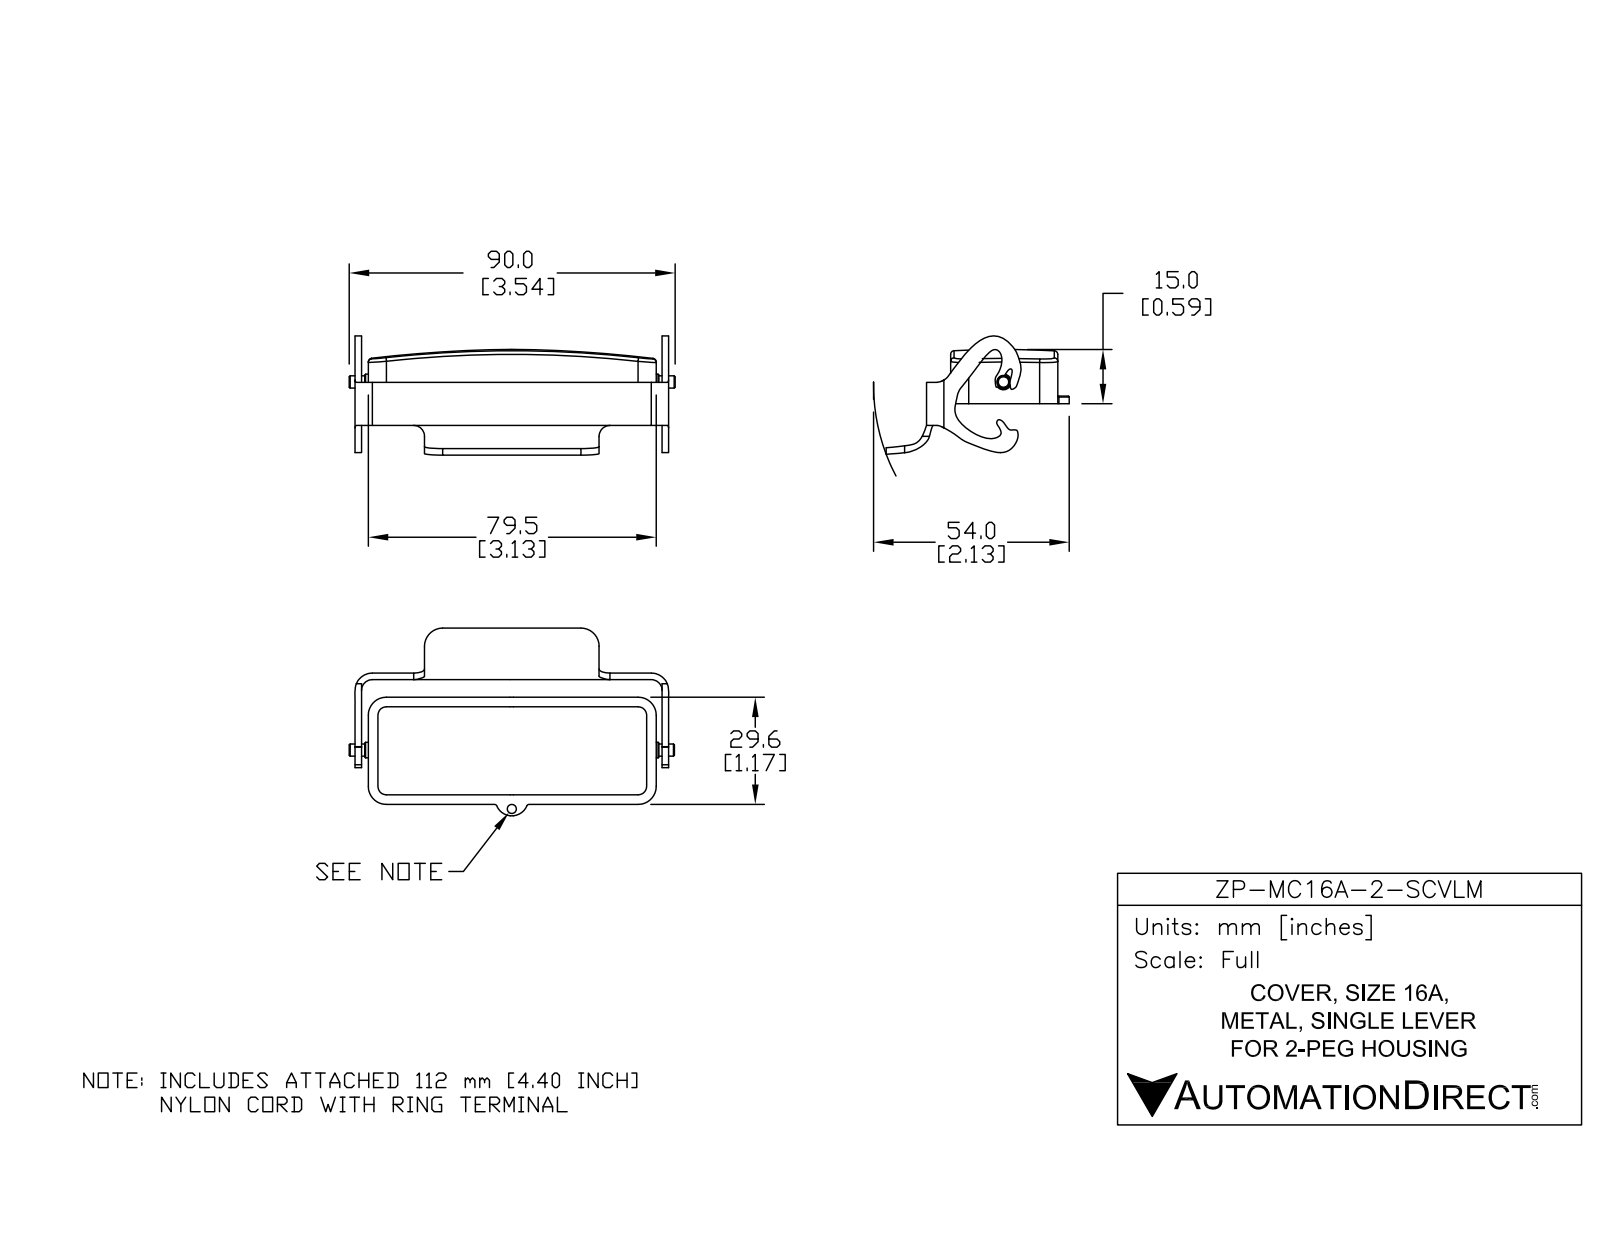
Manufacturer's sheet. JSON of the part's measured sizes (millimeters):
{"part_name": "ZP-MC16A-2-SCVLM", "step_written_by": "SolidWorks 2014 (AUTOMOTIVE_DESIGN)", "units": "millimeters", "bodies": {"solids": 5, "faces": 131, "planar": 47, "cylindrical": 46, "other": 38}, "overall_size": [151.38, 89.79, 66.3], "volume_mm3": 15937, "surface_area_mm2": 15737, "round_holes": [[2.5, 1], [4.1, 1]], "round_bosses_or_shafts": [[4.3, 1], [3.38, 1]], "partial_cylinders_radius": [[5, 6], [0.45, 4], [2.35, 4], [3, 4], [0.5, 2], [0.6, 2], [4.8, 2], [6, 2]], "face_to_face_distances": [2.65, 1.8, 26.95, 6.65, 4.85, 36.25, 34.45, 29.6, 7.5, 9.3]}
